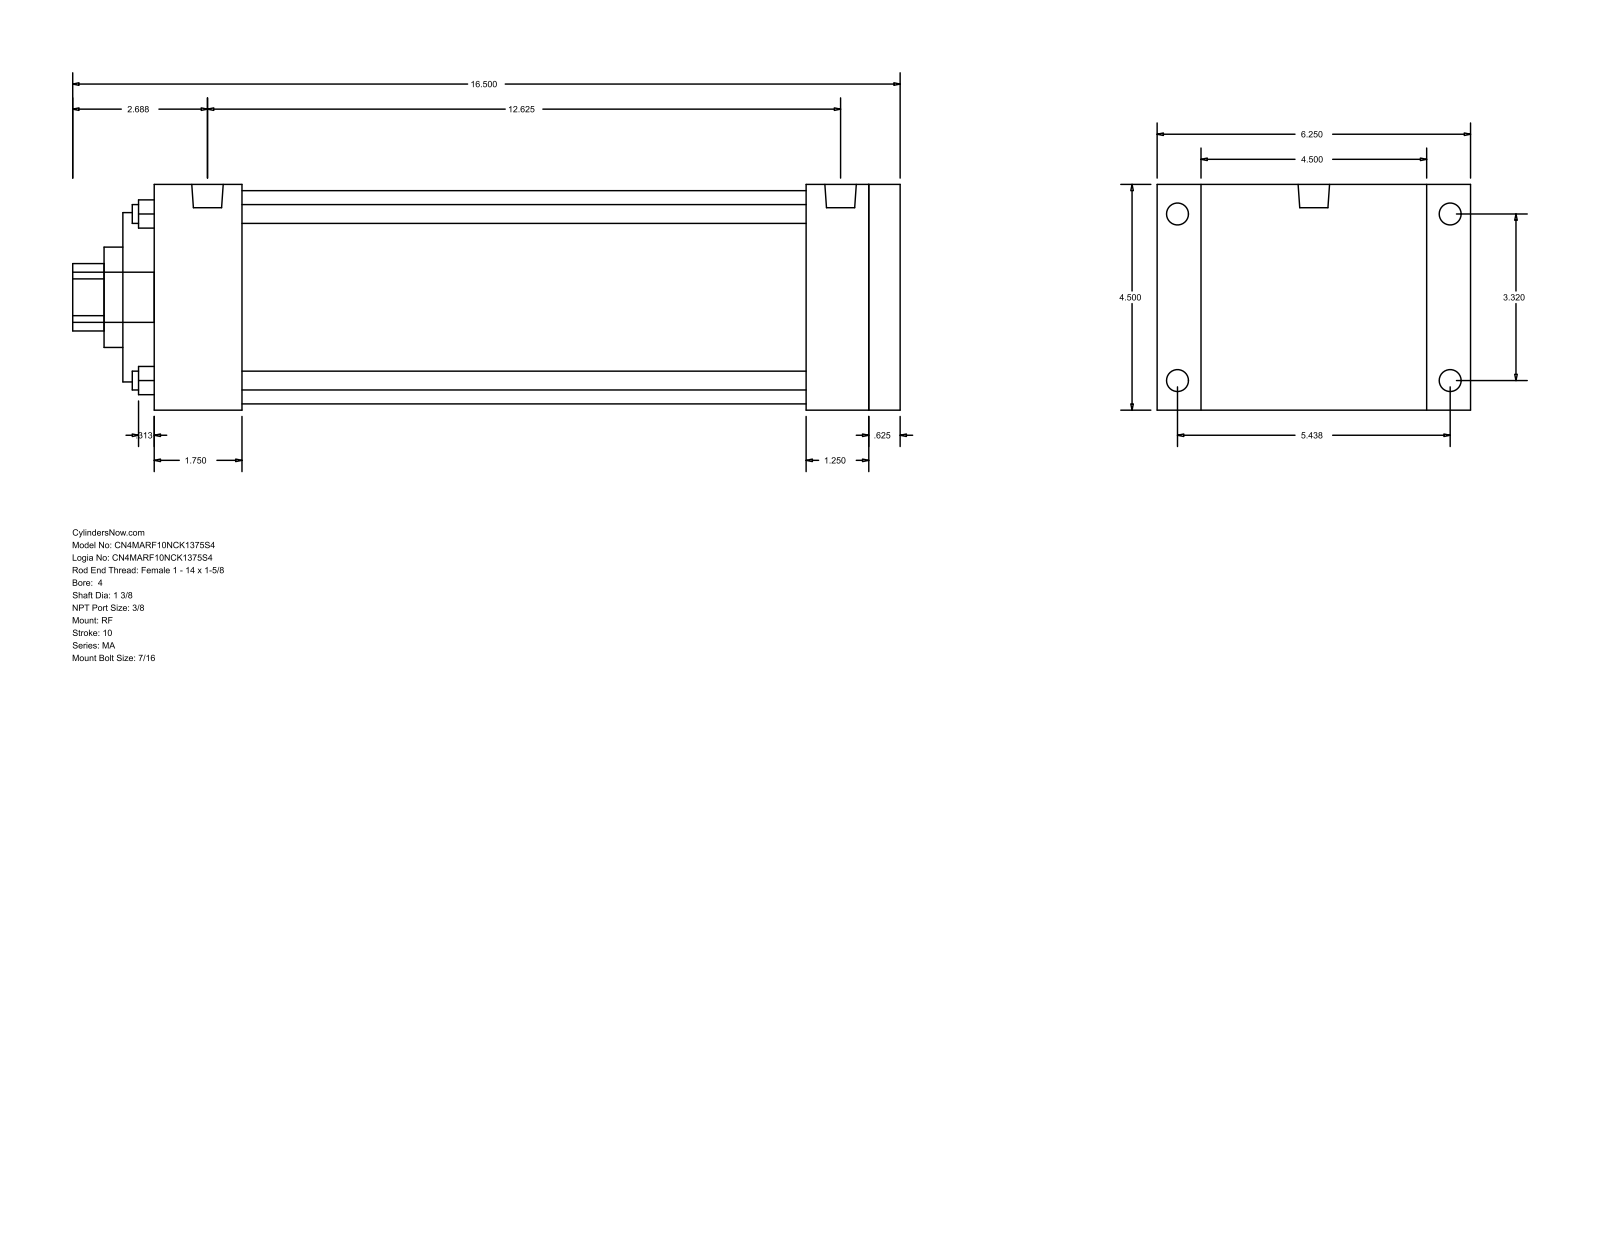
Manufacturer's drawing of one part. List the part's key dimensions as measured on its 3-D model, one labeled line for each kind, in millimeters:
Part name (STEP PRODUCT): MA_RF__0400_1.375
STEP written by: GSSL Pune (CONFIG_CONTROL_DESIGN)
Units: millimetres
Bodies: 0 solids, 94 faces (65 planar, 29 cylindrical, 0 other)
Overall size (bounding box): 419.1 × 158.75 × 114.3
Round holes (diameter × count): ⌀9.53 ×4, ⌀34.92 ×1, ⌀50.8 ×1, ⌀85.72 ×1, ⌀107.95 ×1
Round bosses / shafts (diameter × count): ⌀11.11 ×8, ⌀15.93 ×2, ⌀25.4 ×1
Partial cylindrical surfaces — rounded edges, fillets, slot ends (radius × count): R17.06 ×1
Main face-to-face distances: 114.3, 377.83, 15.87, 361.96, 393.7, 22.23, 136.53, 346.08, 330.21, 31.75
Hole centre spacings: 59.62, 84.32, 119.25
